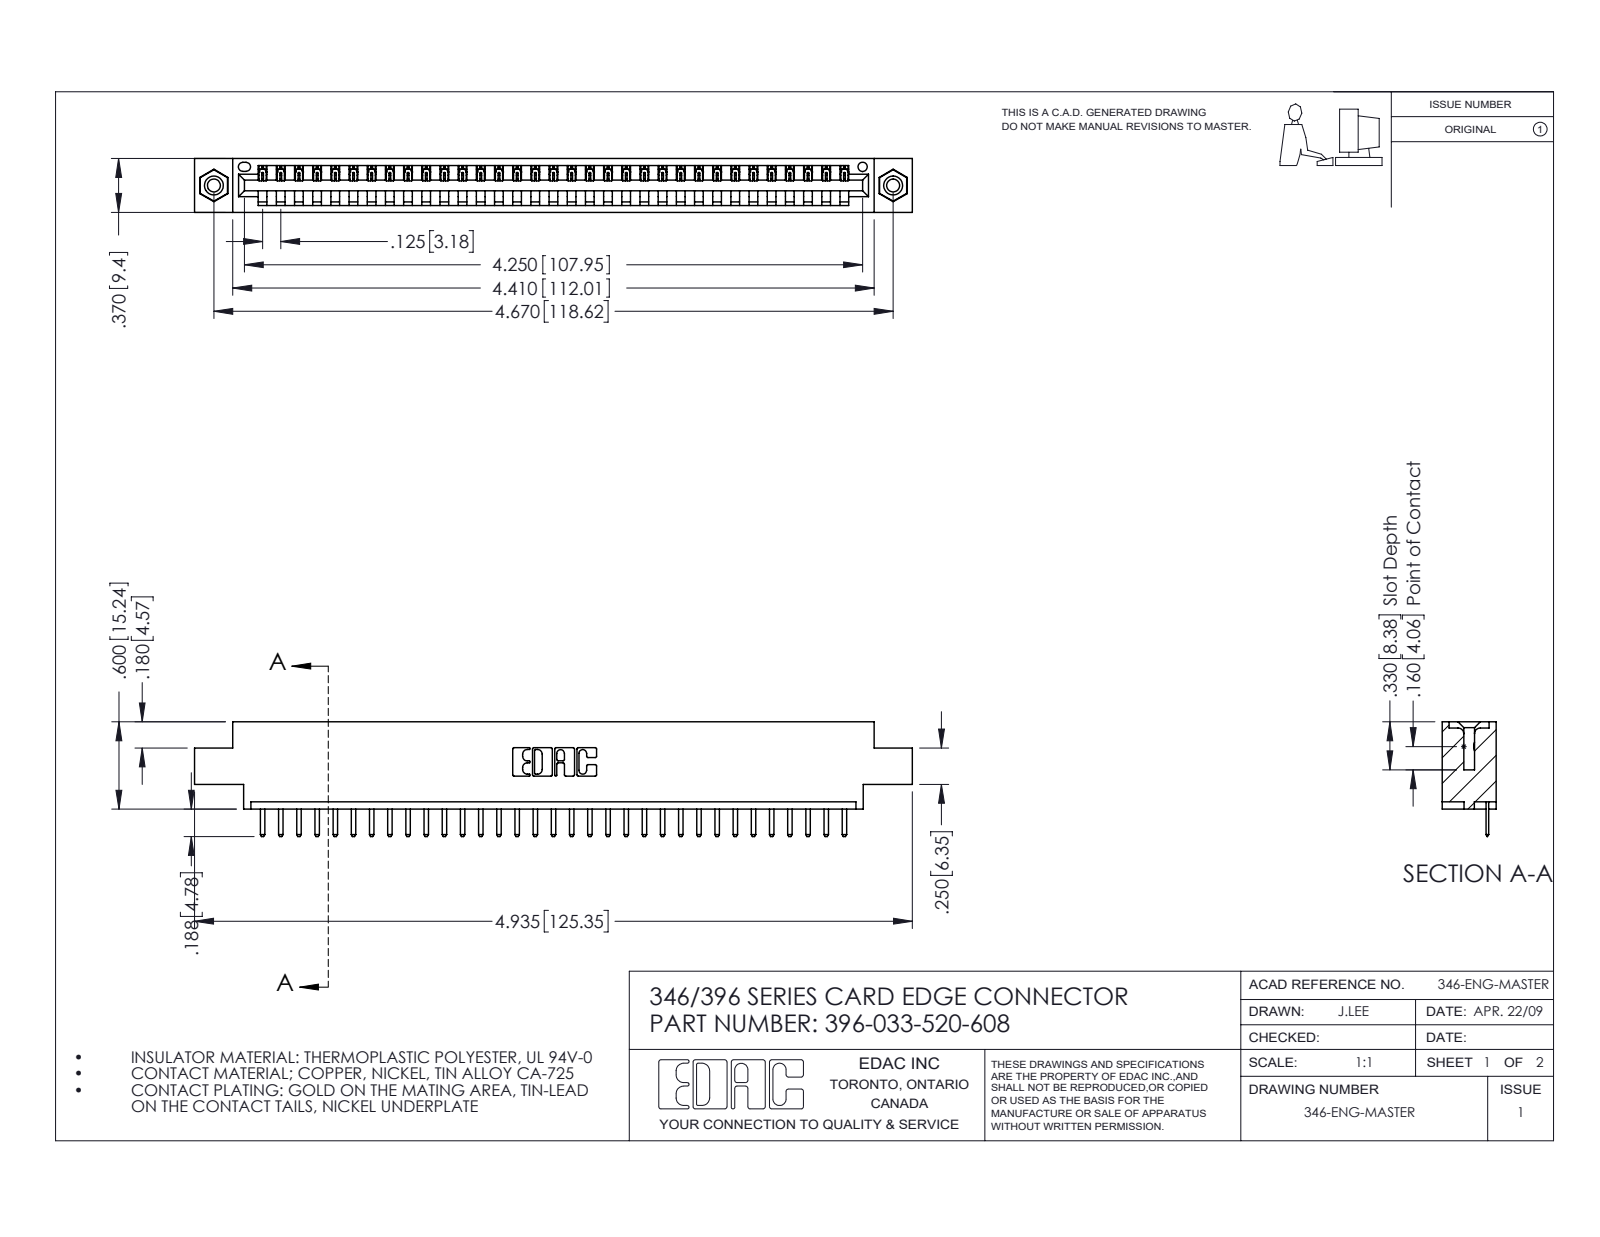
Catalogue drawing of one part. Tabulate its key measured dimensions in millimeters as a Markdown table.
| quantity | value |
| --- | --- |
| part name | 396-033-520-608; 345-292-001_345-293-120; 345-250-001_345-250-003-102; 346 Part_0.170 Offset - 0.156 Dia-TI |
| STEP written by | SolidWorks 2016 (CONFIG_CONTROL_DESIGN) |
| units | millimeters |
| bodies | 36 solids, 2232 faces (1498 planar, 718 cylindrical, 16 other) |
| overall size | 125.3 × 20 × 9.4 |
| volume | 11 700 mm³ |
| surface area | 14 370 mm² |
| round holes (diameter × count) | 2.3 × 2, 3.2 × 2, 4 × 2, 1.6 × 1 |
| round bosses / shafts (diameter × count) | 3.9 × 2 |
| partial cylindrical surfaces (radius × count) | 0.3 × 68, 0.2 × 66, 0.3 × 22, 0.2 × 6, 0.8 × 6, 0.7 × 3, 0.8 × 2, 1 × 2 |
| main face-to-face distances | 1.2, 8.2, 9.4, 6.4, 5.6, 3.8, 2.5, 4.4, 1.8, 7.6 |
| hole center spacings | 6.2, 113.3, 118.6 |
